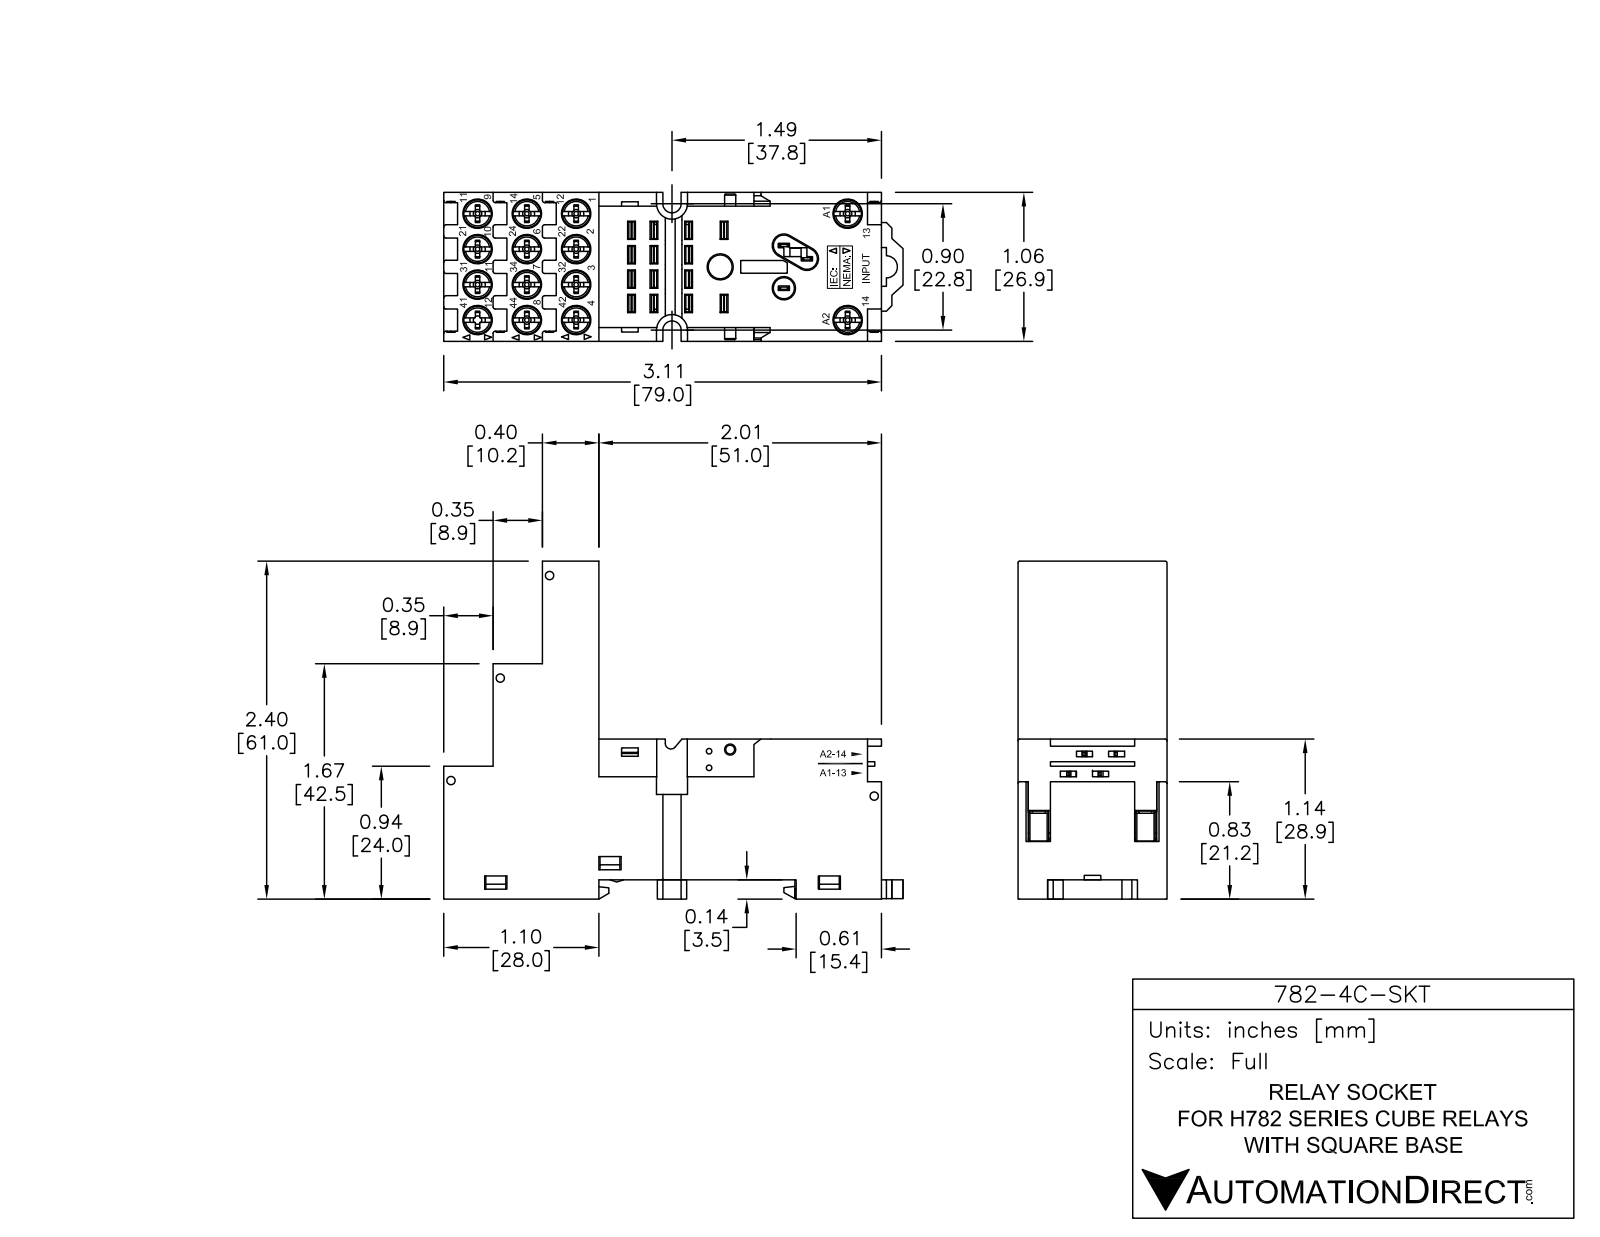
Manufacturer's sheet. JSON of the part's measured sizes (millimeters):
{"part_name": "782-4C-SKT", "step_written_by": "SolidWorks 2013 (AUTOMOTIVE_DESIGN)", "units": "millimeters", "bodies": {"solids": 18, "faces": 846, "planar": 677, "cylindrical": 117, "other": 52}, "overall_size": [81.71, 60.75, 27.02], "volume_mm3": 57857, "surface_area_mm2": 22503, "round_holes": [[5.1, 12], [5.15, 2], [3.81, 1], [4.25, 1]], "partial_cylinders_radius": [[0.5, 24], [1.78, 3], [2.78, 2], [3.17, 2], [3.61, 2], [0.35, 1], [0.39, 1], [0.48, 1]], "face_to_face_distances": [27, 6.38, 5.5, 3.85, 12.76, 2, 25.44, 6, 10.23, 2.53], "hole_center_spacings": [6.38, 11.26, 19.41, 12.76, 9.05, 9.28, 15.78, 18.33]}
